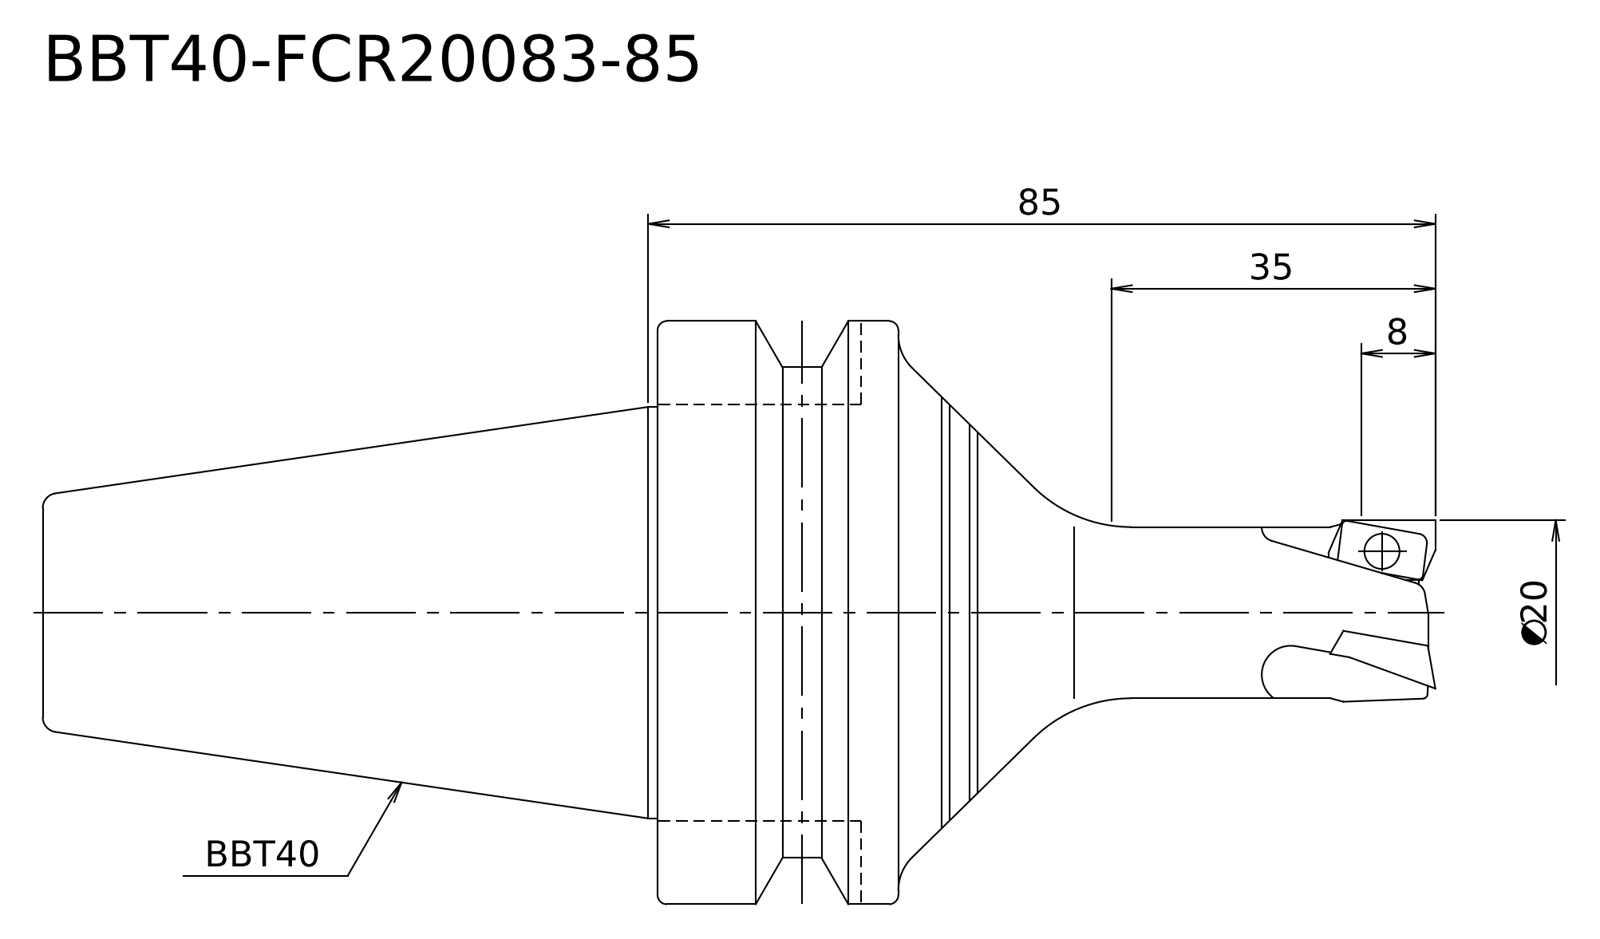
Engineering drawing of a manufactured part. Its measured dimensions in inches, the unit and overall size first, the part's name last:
Units: inches
Overall size (bounding box): 5.921 × 2.48 × 2.48
Round bosses / shafts (diameter × count): ⌀2.48 ×1, ⌀2.087 ×1, ⌀1.75 ×1, ⌀0.787 ×1, ⌀0.728 ×1
Main face-to-face distances: 2.614, 3.307, 5.921, 2.283, 1.024, 3.638
Volume: 10.66 in³ · Surface area: 33.8 in²
Bodies: 1 solid, 17 faces (4 planar, 6 cylindrical, 7 other)
STEP written by: Kubotek KeyCreator V8.5.1 (14335) (CONFIG_CONTROL_DESIGN)
